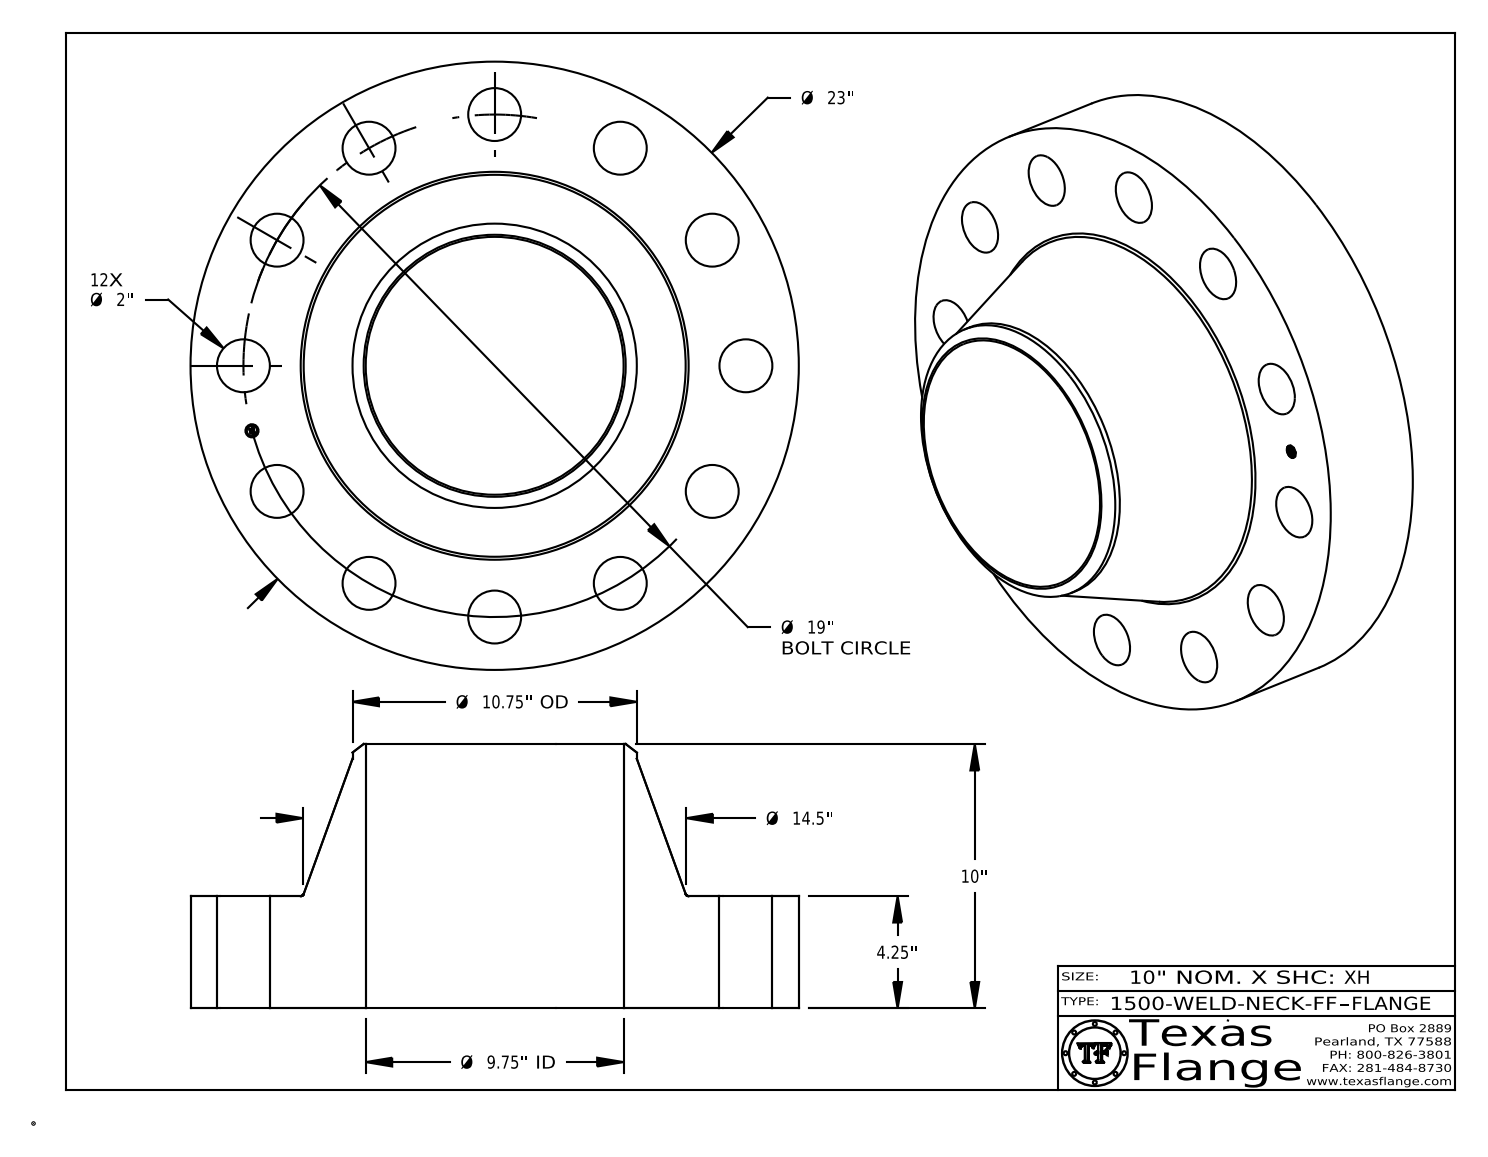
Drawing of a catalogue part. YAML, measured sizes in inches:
part_name: "1500-WELD-NECK-FF"
step_written_by: "CATIA V5 STEP AP214 (AUTOMOTIVE_DESIGN)"
units: inches
bodies: {solids: 1, faces: 424, planar: 368, cylindrical: 50, other: 6}
overall_size: [23, 23, 10]
volume: 1562
surface_area: 1695
round_holes:
  - {diameter: 2, count: 12}
  - {diameter: 0.495, count: 1}
  - {diameter: 9.75, count: 1}
round_bosses_or_shafts:
  - {diameter: 0.03, count: 8}
  - {diameter: 23, count: 1}
  - {diameter: 10.75, count: 1}
  - {diameter: 0.39, count: 1}
face_to_face_distances: [4.25, 10, 5.75, 4.235, 0.015, 5.765, 0.148, 0.144, 0.027, 0.096]
hole_center_spacings: [9.5, 13.435, 16.454, 18.352, 4.918, 19, 4.917, 15.074]
